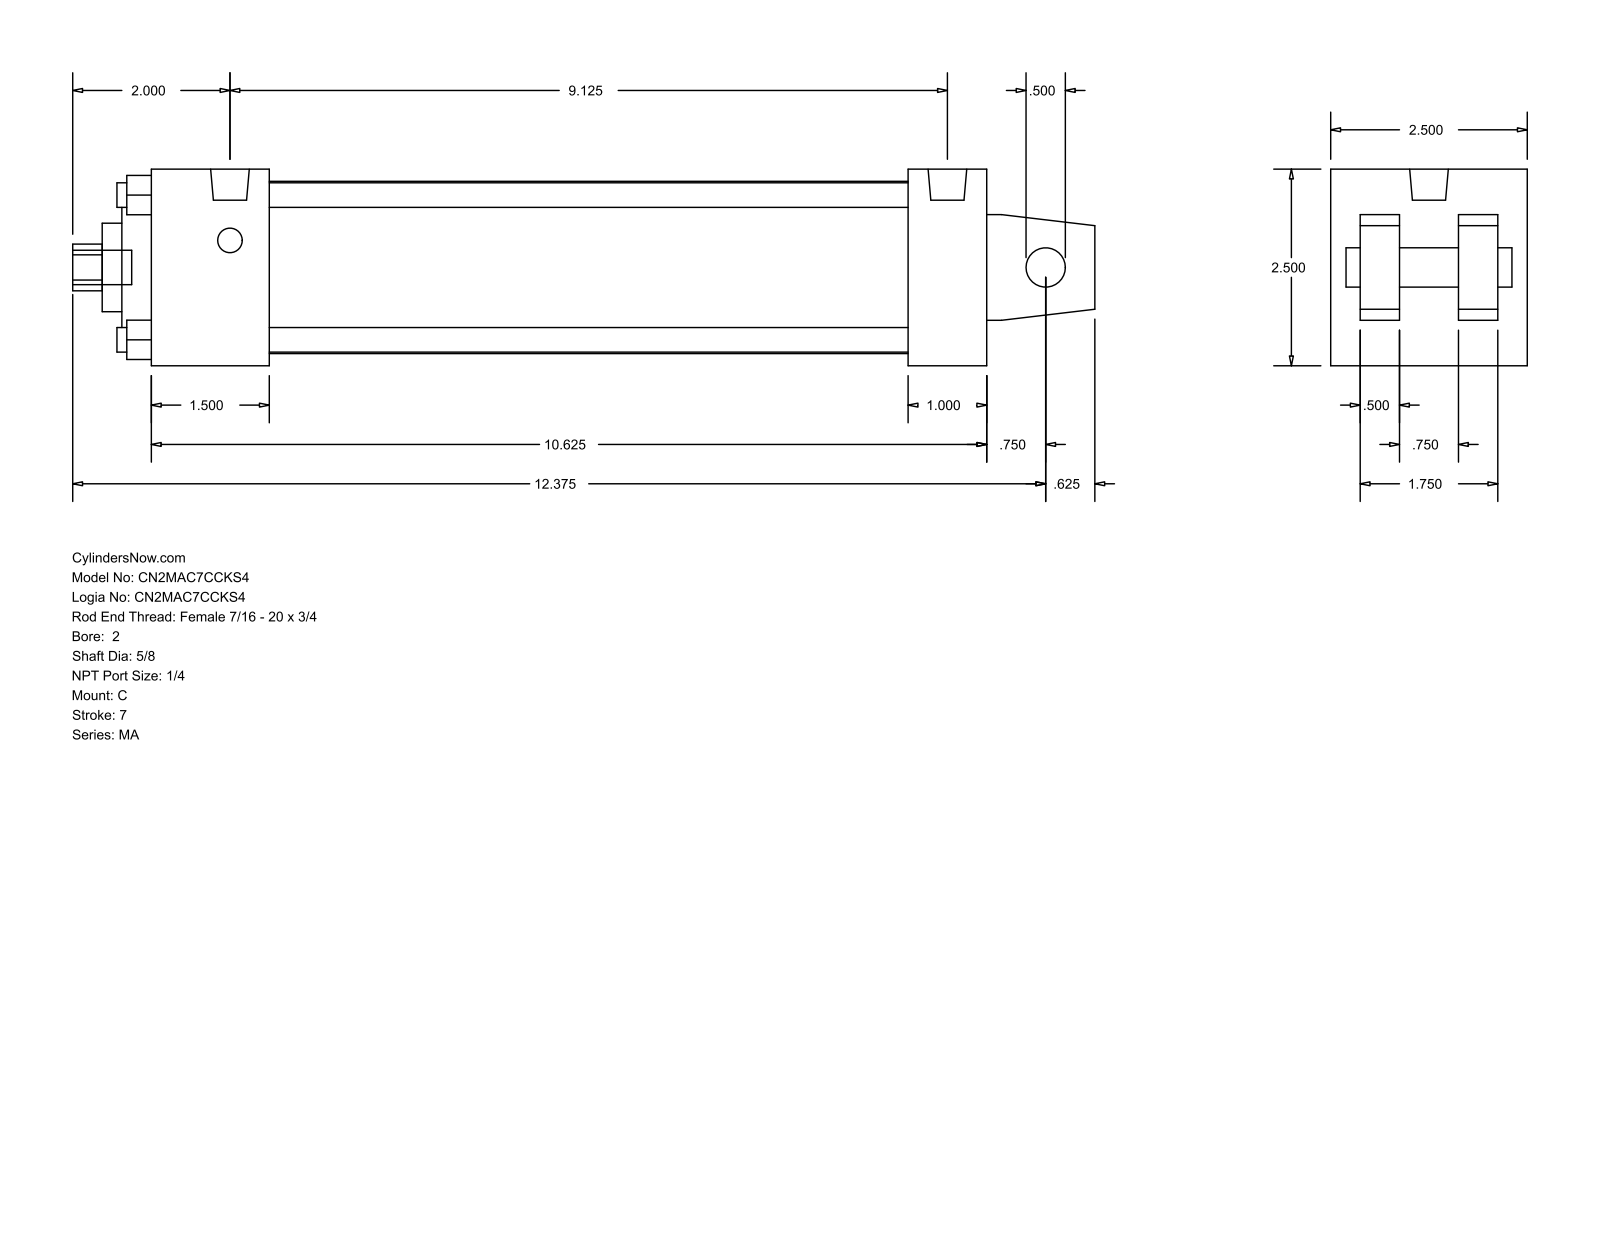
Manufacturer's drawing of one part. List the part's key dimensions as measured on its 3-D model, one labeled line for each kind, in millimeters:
Part name (STEP PRODUCT): MA_C__0200_0.625
STEP written by: GSSL Pune (CONFIG_CONTROL_DESIGN)
Units: millimetres
Bodies: 0 solids, 105 faces (77 planar, 28 cylindrical, 0 other)
Overall size (bounding box): 330.2 × 63.5 × 63.5
Round holes (diameter × count): ⌀7.94 ×4, ⌀12.7 ×1, ⌀15.88 ×1, ⌀28.57 ×1, ⌀50.8 ×1, ⌀55.63 ×1
Round bosses / shafts (diameter × count): ⌀7.94 ×4, ⌀12.49 ×2, ⌀11.11 ×1
Partial cylindrical surfaces — rounded edges, fillets, slot ends (radius × count): R7.54 ×1
Main face-to-face distances: 63.5, 9.52, 12.7, 22.22, 41.28, 53.98, 31.76, 38.1, 269.87, 231.77
Hole centre spacings: 33.05, 46.74, 66.1
